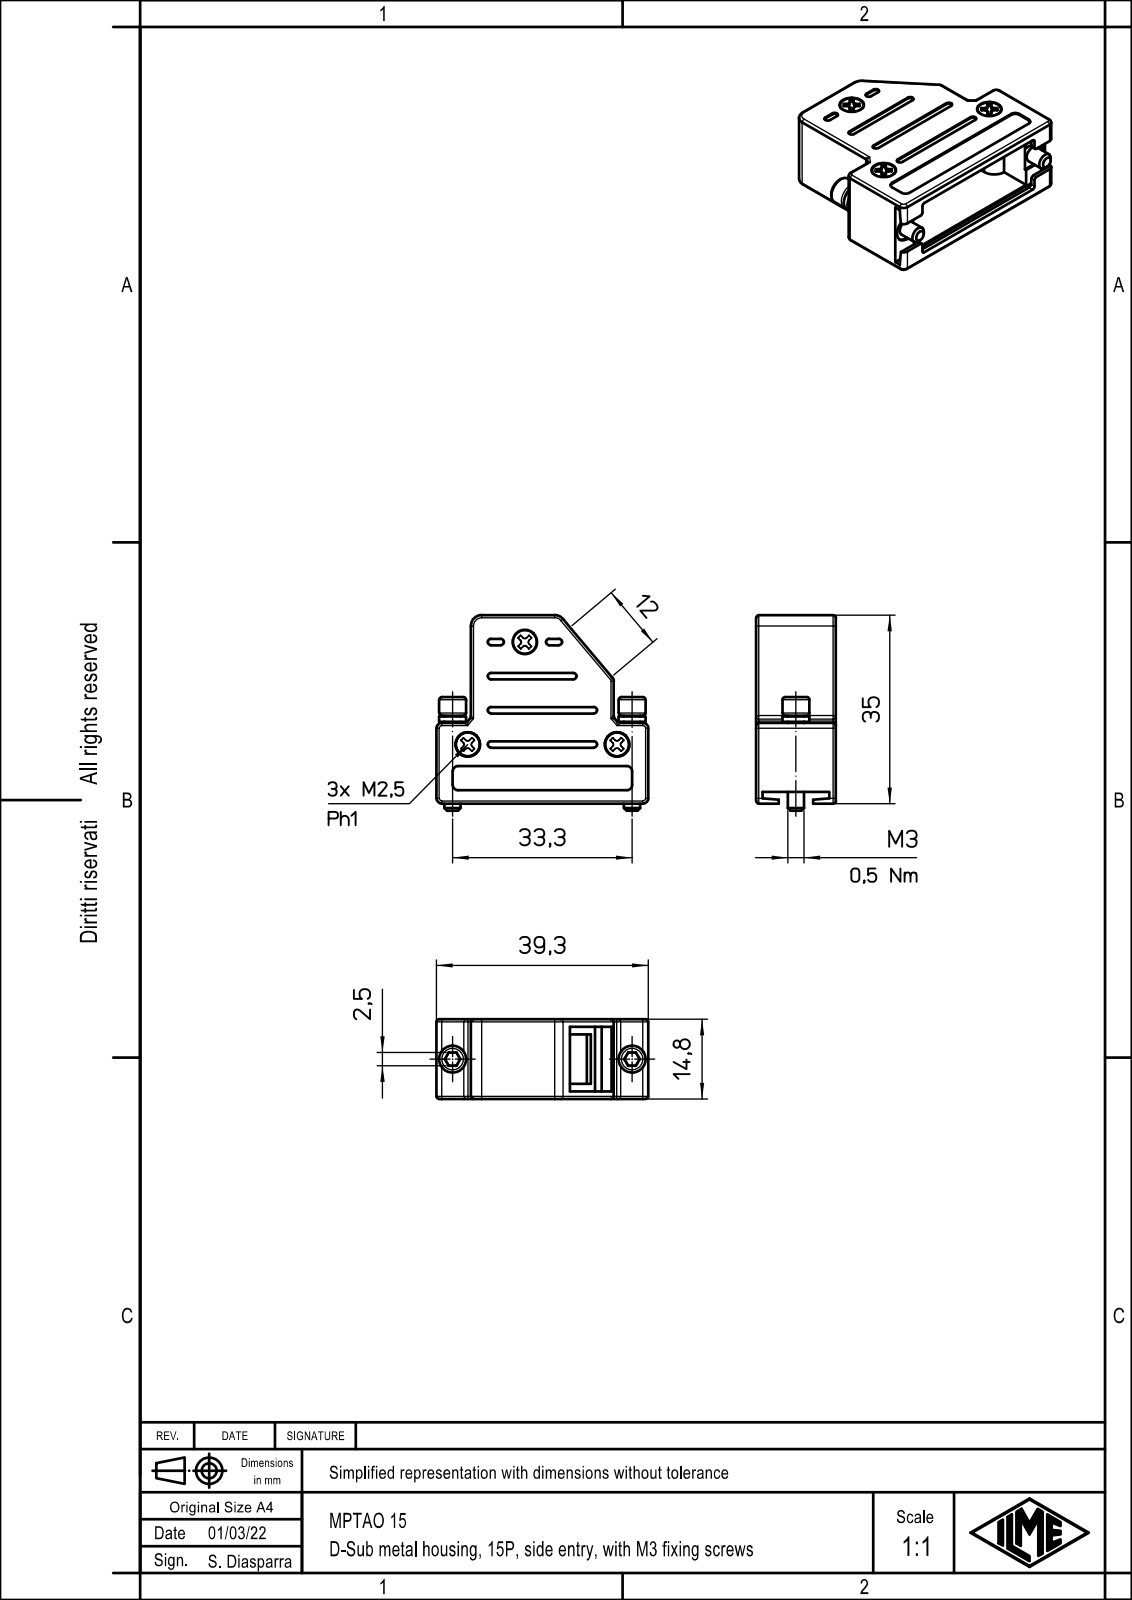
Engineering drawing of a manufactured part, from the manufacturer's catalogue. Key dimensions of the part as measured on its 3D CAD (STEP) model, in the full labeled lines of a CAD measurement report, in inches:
Part name (STEP PRODUCT): MPTAO_15
STEP written by: Creo Elements/Direct Modeling 20.1B 02-Apr-2019 (C) Parametric Technology GmbH (AUTOMOTIVE_DESIGN)
Units: inches
Bodies: 1 solid, 633 faces (156 planar, 203 cylindrical, 274 other)
Overall size (bounding box): 1.547 × 1.429 × 0.583
Volume: 0.418 in³ · Surface area: 10.63 in²
Round bosses / shafts (diameter × count): ⌀0.197 ×2, ⌀0.118 ×2
Partial cylindrical surfaces — rounded edges, fillets, slot ends (radius × count): R0.02 ×40, R0.039 ×13, R0.024 ×10, R0.079 ×2, R0.083 ×2, R0.1 ×2
Main face-to-face distances: 0.059, 0.524, 0.583, 0.465, 0.051, 0.516, 0.575, 0.047, 0.252, 0.567
